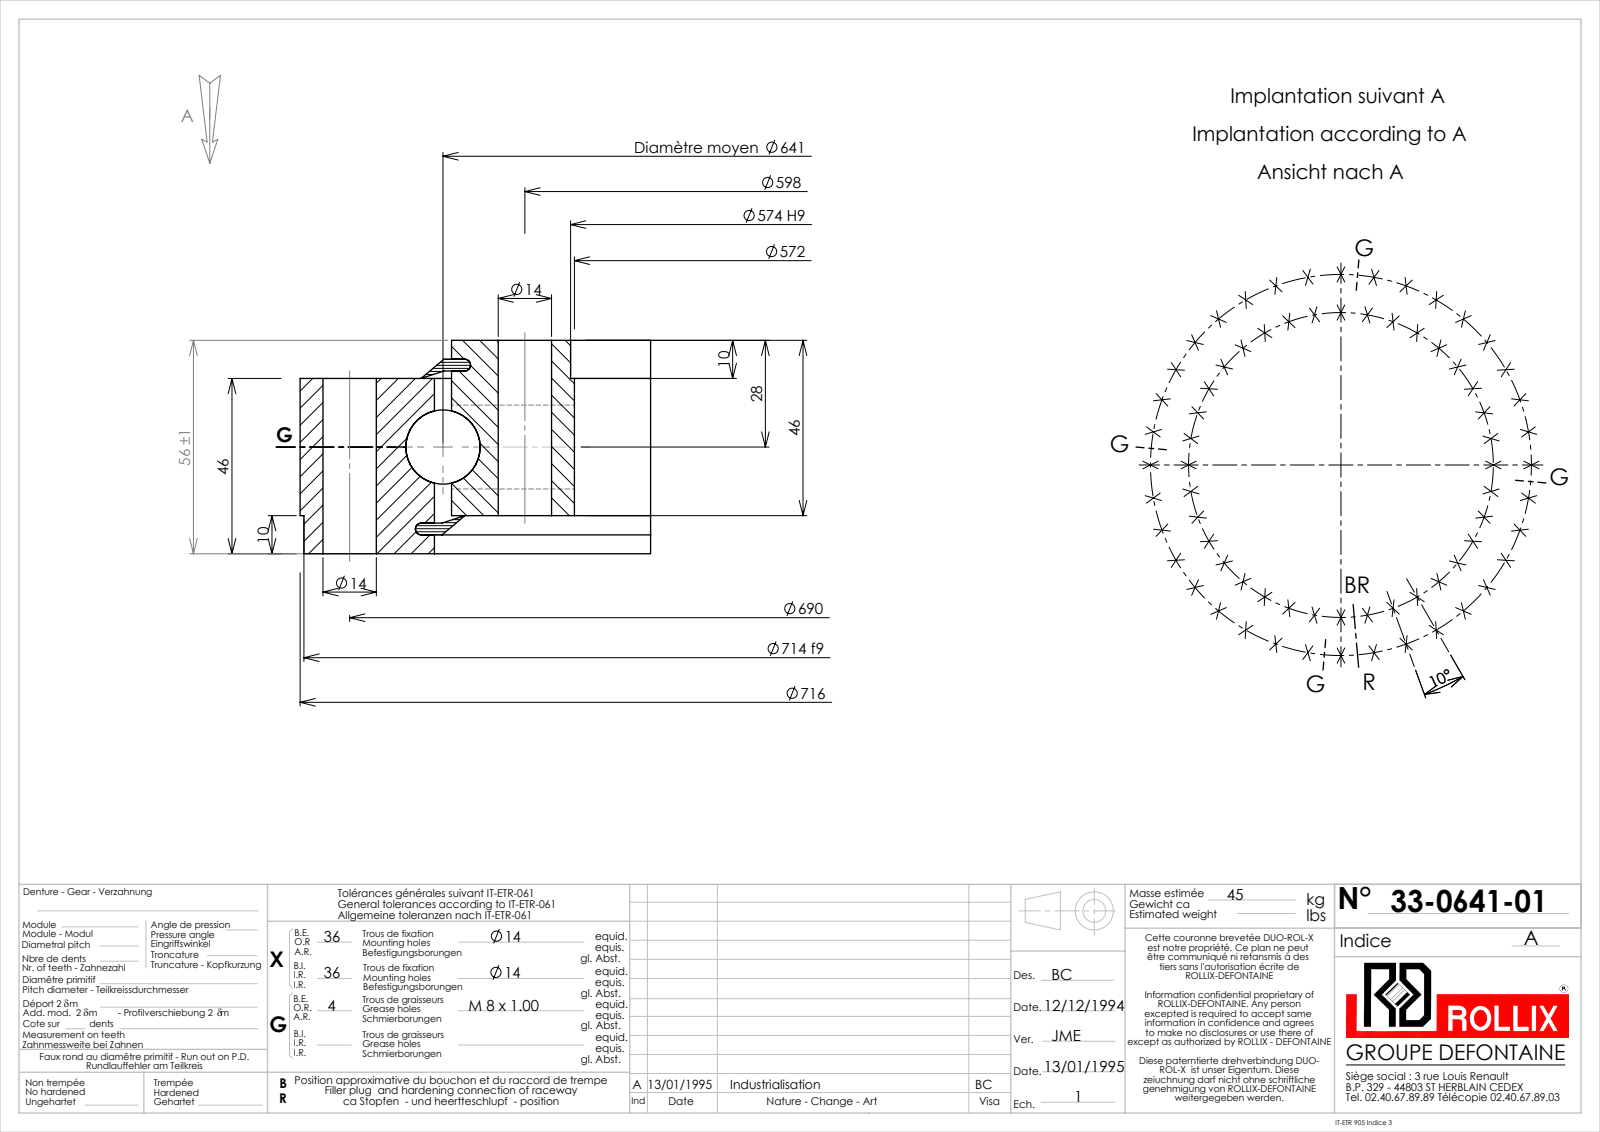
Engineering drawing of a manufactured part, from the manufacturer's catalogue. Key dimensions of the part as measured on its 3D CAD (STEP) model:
Part name (STEP PRODUCT): 33-0641-01
STEP written by: SolidWorks 2016 (CONFIG_CONTROL_DESIGN)
Units: millimetres
Bodies: 9 solids, 302 faces (54 planar, 180 cylindrical, 68 other)
Overall size (bounding box): 732.81 × 732.81 × 56
Volume: 5 372 000 mm³ · Surface area: 957 411 mm²
Round holes (diameter × count): ⌀14 ×72, ⌀7 ×4, ⌀572 ×1, ⌀574 ×1, ⌀645.5 ×1
Round bosses / shafts (diameter × count): ⌀8 ×4, ⌀716 ×1, ⌀714 ×1, ⌀636.5 ×1
Main face-to-face distances: 46, 10, 36, 56, 4.95, 51.05, 5.05, 41.05, 8.05, 47.95
Hole centre spacings: 103.84, 422.85, 489.85, 154.77, 52.12, 541.97, 343, 517.88
